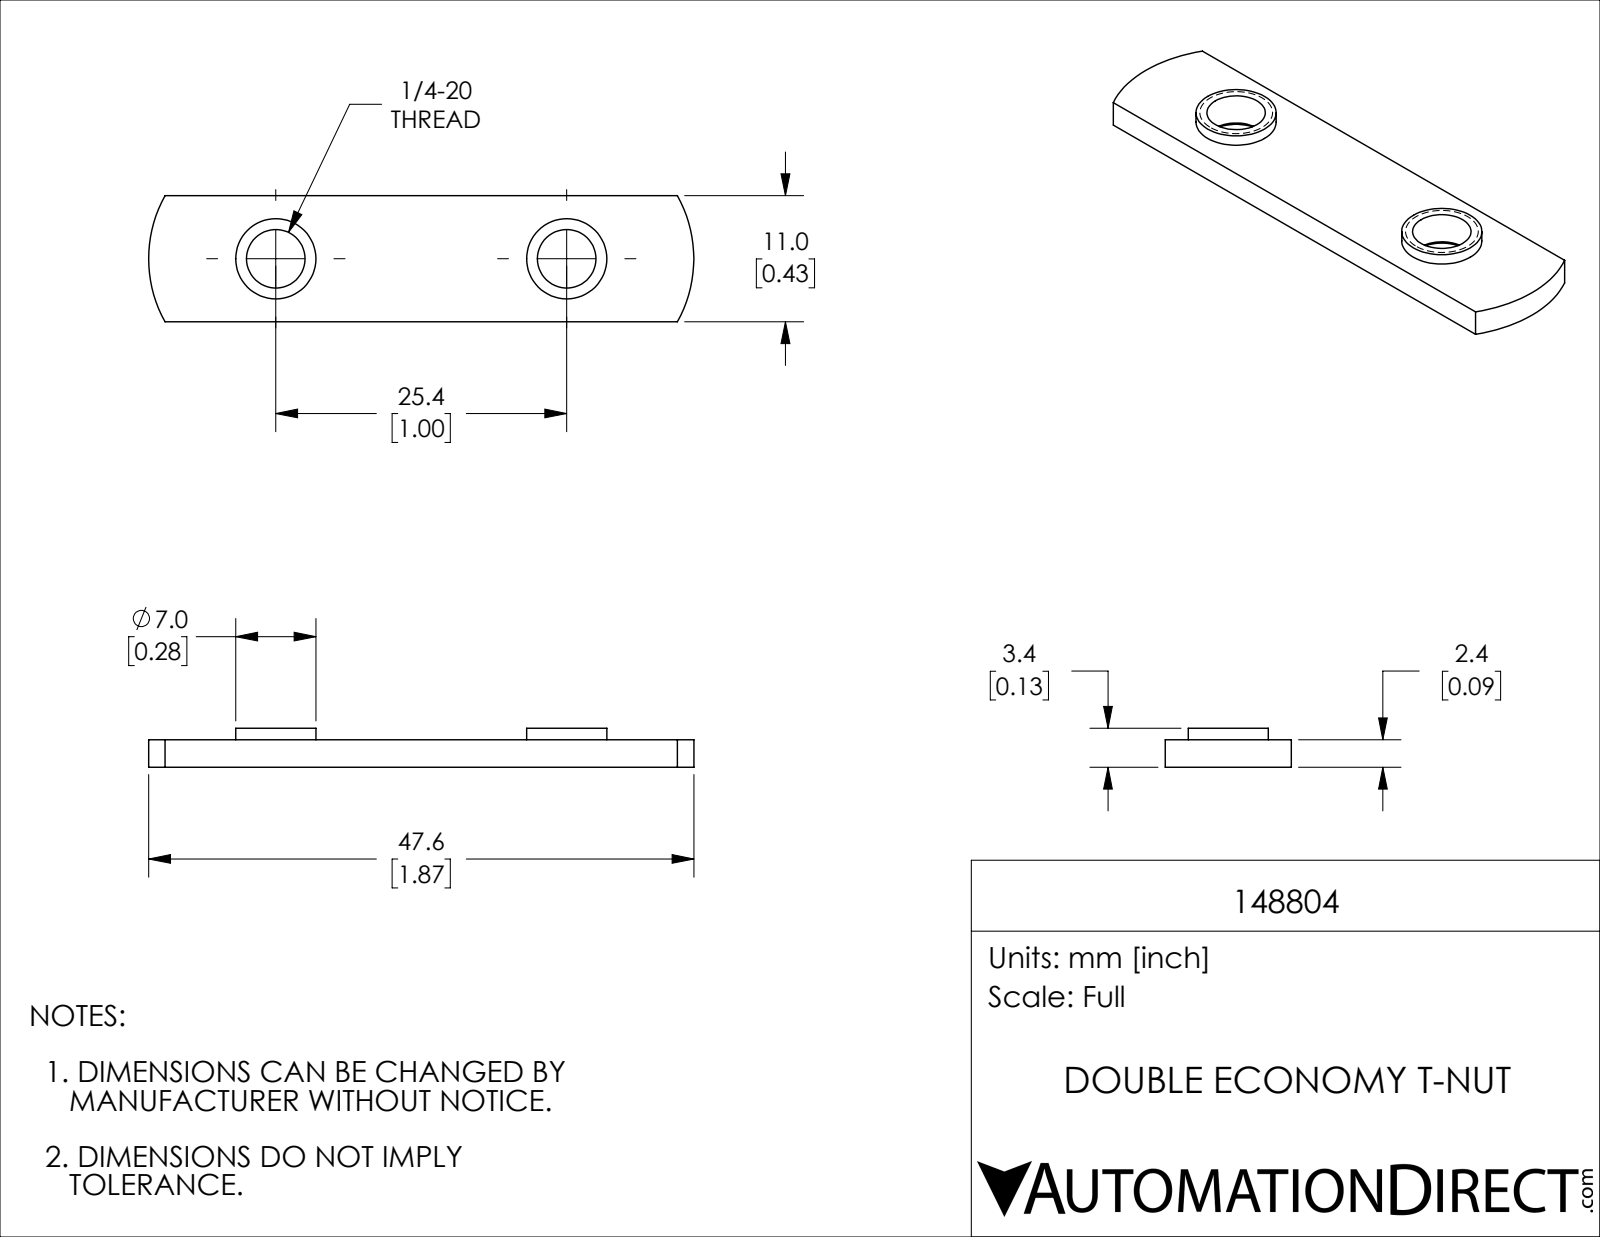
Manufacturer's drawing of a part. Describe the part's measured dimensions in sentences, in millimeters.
The part is named "148804". Its 3-D file was written by "SolidWorks 2021 (CONFIG_CONTROL_DESIGN)". It is 1 solid with 21 faces: 6 planar, 11 cylindrical and 4 other. Overall it measures 47.6 by 11 by 3.4 millimeters. Its volume is 1 166 cubic millimeters and its surface area 1 359 square millimeters. Round holes: 2 of diameter 5.11. Round bosses or shafts: 2 of diameter 7. Partial cylindrical surfaces (rounded edges, fillets, slot ends): 2 of radius 11.3. The main face-to-face distances are 2.4, 11, 1, 3.4. The hole center spacings are 25.4.
